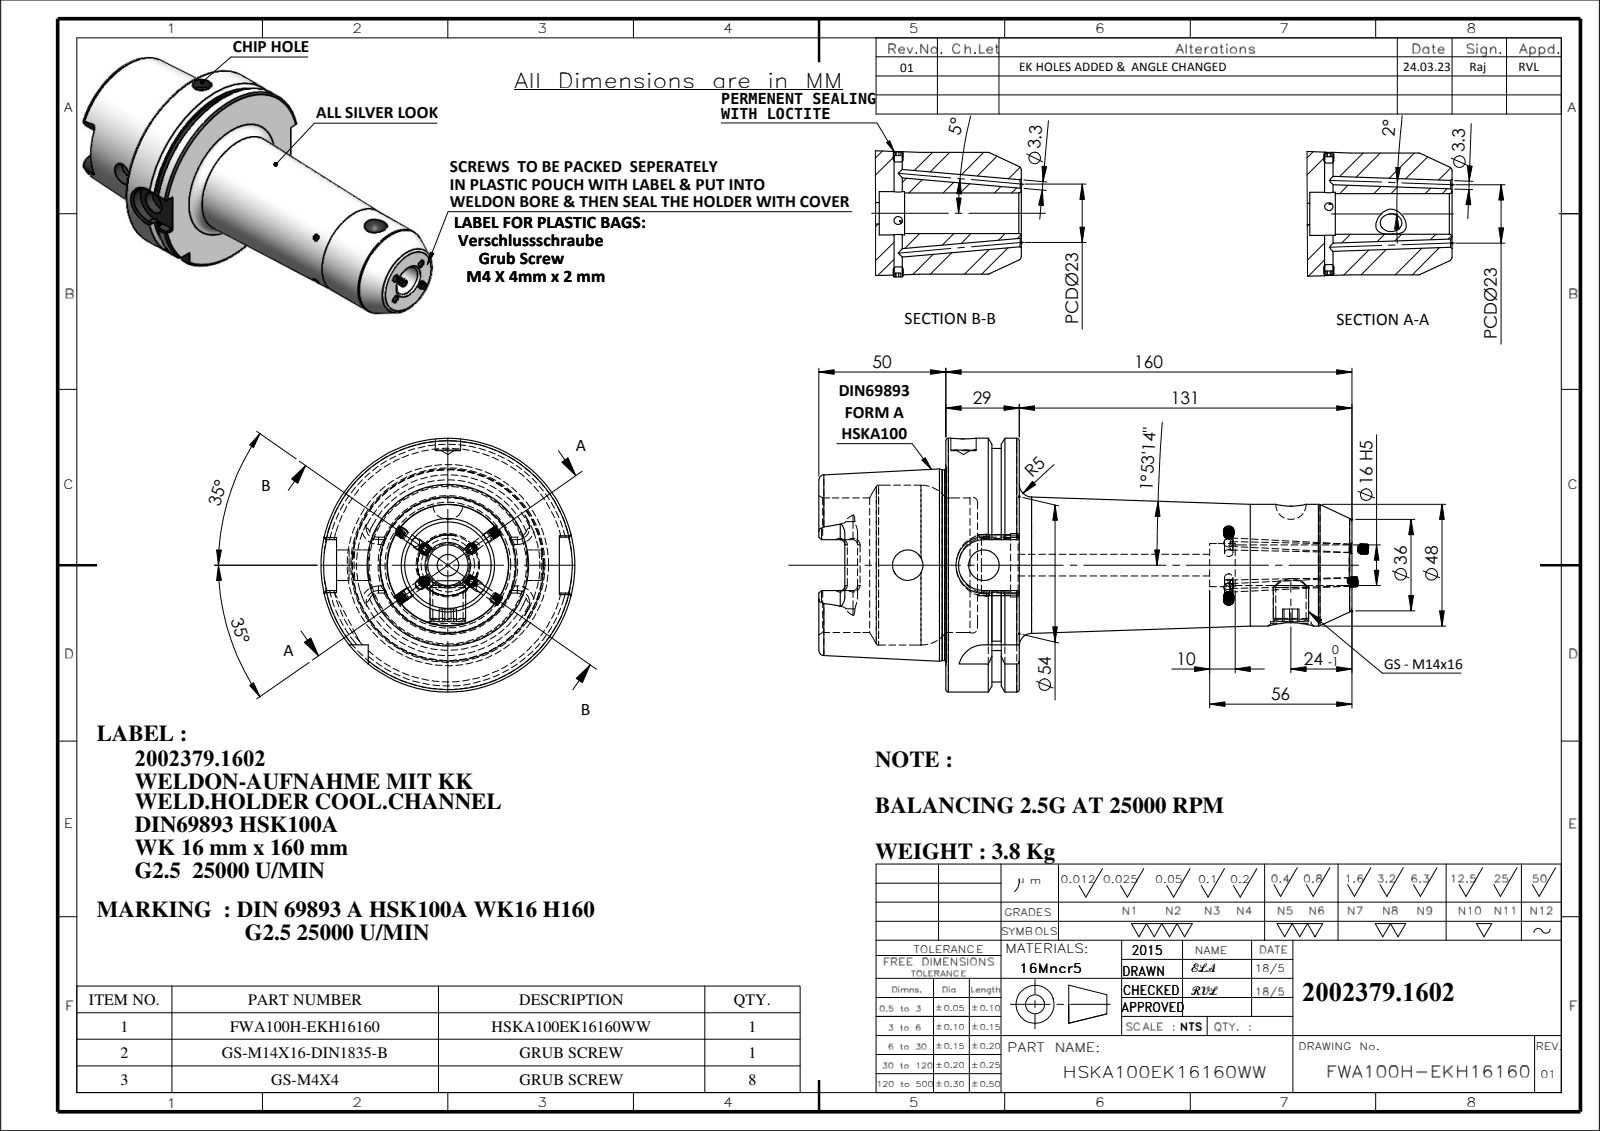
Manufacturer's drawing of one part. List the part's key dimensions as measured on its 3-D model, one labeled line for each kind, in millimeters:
Part name (STEP PRODUCT): HSKA100EK16160WW_ISO; GS-M14X16-DIN1835-B_ISO 4026 - M12 x 12-N; HSKA100EK16160WW; GS-M4X4_DIN 913 - M4 x 4-N (+1 more)
STEP written by: SolidWorks 2018 (CONFIG_CONTROL_DESIGN)
Units: millimetres
Bodies: 10 solids, 611 faces (139 planar, 156 cylindrical, 316 other)
Overall size (bounding box): 218.11 × 100 × 100
Volume: 489 783 mm³ · Surface area: 78 314 mm²
Round holes (diameter × count): ⌀3.3 ×8, ⌀12 ×3, ⌀16 ×2, ⌀8.5 ×1, ⌀10 ×1, ⌀17 ×1, ⌀21 ×1, ⌀25 ×1, ⌀53 ×1, ⌀63 ×1
Round bosses / shafts (diameter × count): ⌀4 ×8, ⌀100 ×1, ⌀92 ×1, ⌀75.16 ×1, ⌀48 ×1, ⌀14 ×1
Partial cylindrical surfaces — rounded edges, fillets, slot ends (radius × count): R1.8 ×6, R4.88 ×4, R10 ×2, R11 ×1
Main face-to-face distances: 28.95, 12.5, 16.45, 50, 62.5, 78.95, 210, 160, 147.5, 131.05
Hole centre spacings: 0.97, 30, 129
